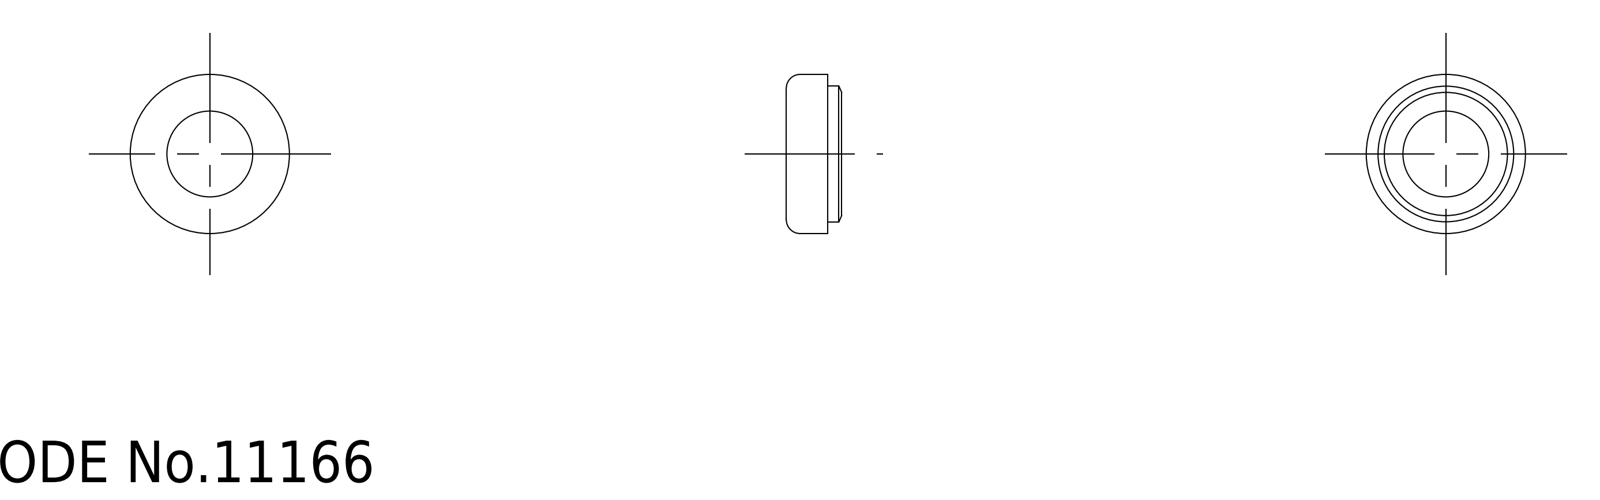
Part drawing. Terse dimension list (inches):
name: TL_421_M6; washer; packing
written by: SolidWorks 2015 (AUTOMOTIVE_DESIGN)
unit: in
bodies: 2 solids, 22 faces (6 planar, 12 cylindrical, 4 other)
size: 0.453 × 0.453 × 0.157
volume: 0.016 in³; area: 0.857 in²
holes: 1× ⌀0.244, 1× ⌀0.374
bosses: 1× ⌀0.453, 1× ⌀0.386
face distances: 0.039, 0.118, 0.079, 0.157
